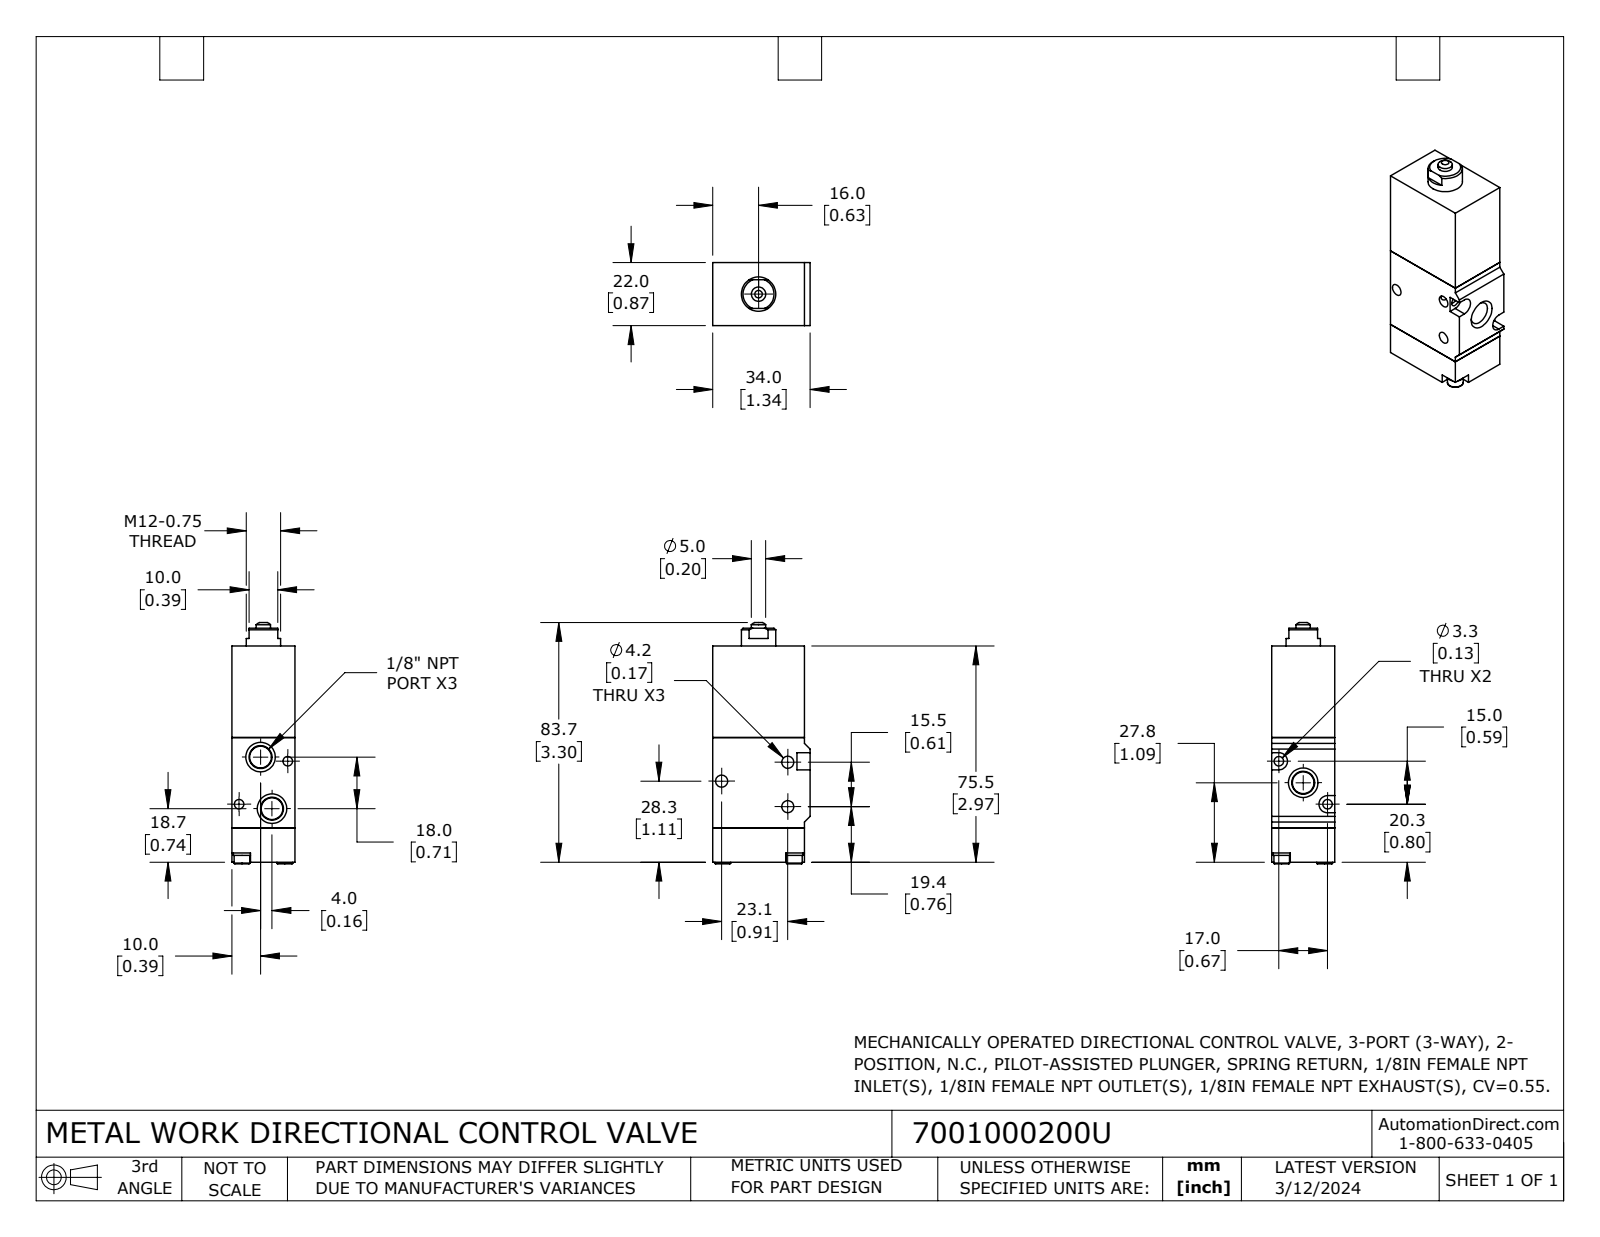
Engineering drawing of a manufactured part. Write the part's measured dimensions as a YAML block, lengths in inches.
part_name: "7001000200U"
step_written_by: "SolidWorks 2023 (CONFIG_CONTROL_DESIGN)"
units: inches
bodies: {solids: 7, faces: 159, planar: 77, cylindrical: 38, other: 44}
overall_size: [3.319, 1.339, 0.866]
volume: 3.187
surface_area: 23.52
round_holes:
  - {diameter: 0.165, count: 3}
  - {diameter: 0.118, count: 2}
  - {diameter: 0.13, count: 2}
round_bosses_or_shafts:
  - {diameter: 0.236, count: 2}
  - {diameter: 0.217, count: 2}
  - {diameter: 0.472, count: 1}
  - {diameter: 0.197, count: 1}
partial_cylinders:
  - {radius: 0.118, count: 2}
face_to_face_distances: [0.866, 1.26, 1.24, 0.472, 1.713, 2.972, 2.5, 0.079, 1.339, 0.311]
hole_center_spacings: [0.61, 0.893, 0.946, 0.975, 1.148]
